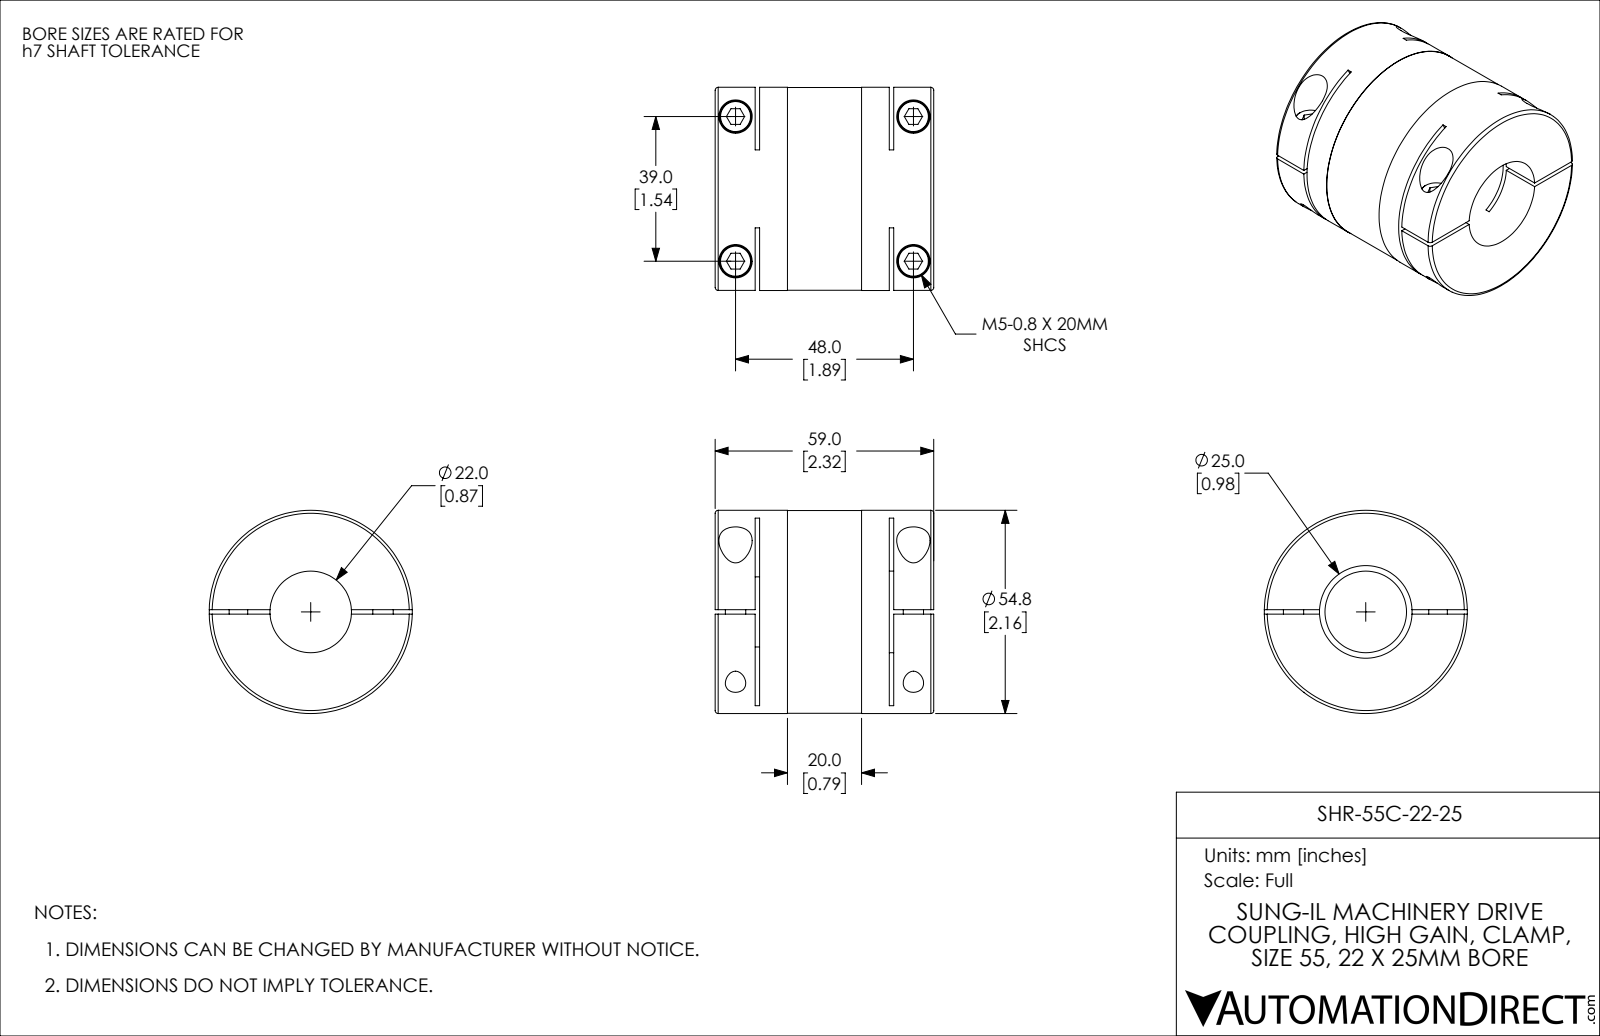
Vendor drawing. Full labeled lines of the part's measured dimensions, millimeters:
Part name (STEP PRODUCT): SHR-55C-22-25
STEP written by: SolidWorks 2021 (CONFIG_CONTROL_DESIGN)
Units: millimetres
Bodies: 1 solid, 144 faces (70 planar, 58 cylindrical, 16 other)
Overall size (bounding box): 59 × 54.8 × 54.8
Volume: 103 579 mm³ · Surface area: 28 620 mm²
Round holes (diameter × count): ⌀5.5 ×4, ⌀9 ×4, ⌀22 ×1, ⌀25 ×1, ⌀27 ×1
Round bosses / shafts (diameter × count): ⌀8.5 ×4, ⌀5 ×2, ⌀54.8 ×1, ⌀54.7 ×1
Partial cylindrical surfaces — rounded edges, fillets, slot ends (radius × count): R60 ×2
Main face-to-face distances: 1.2, 12, 47, 10.8, 48.2, 36.2, 59, 35, 37.4, 19.5
Hole centre spacings: 39, 48, 61.85
